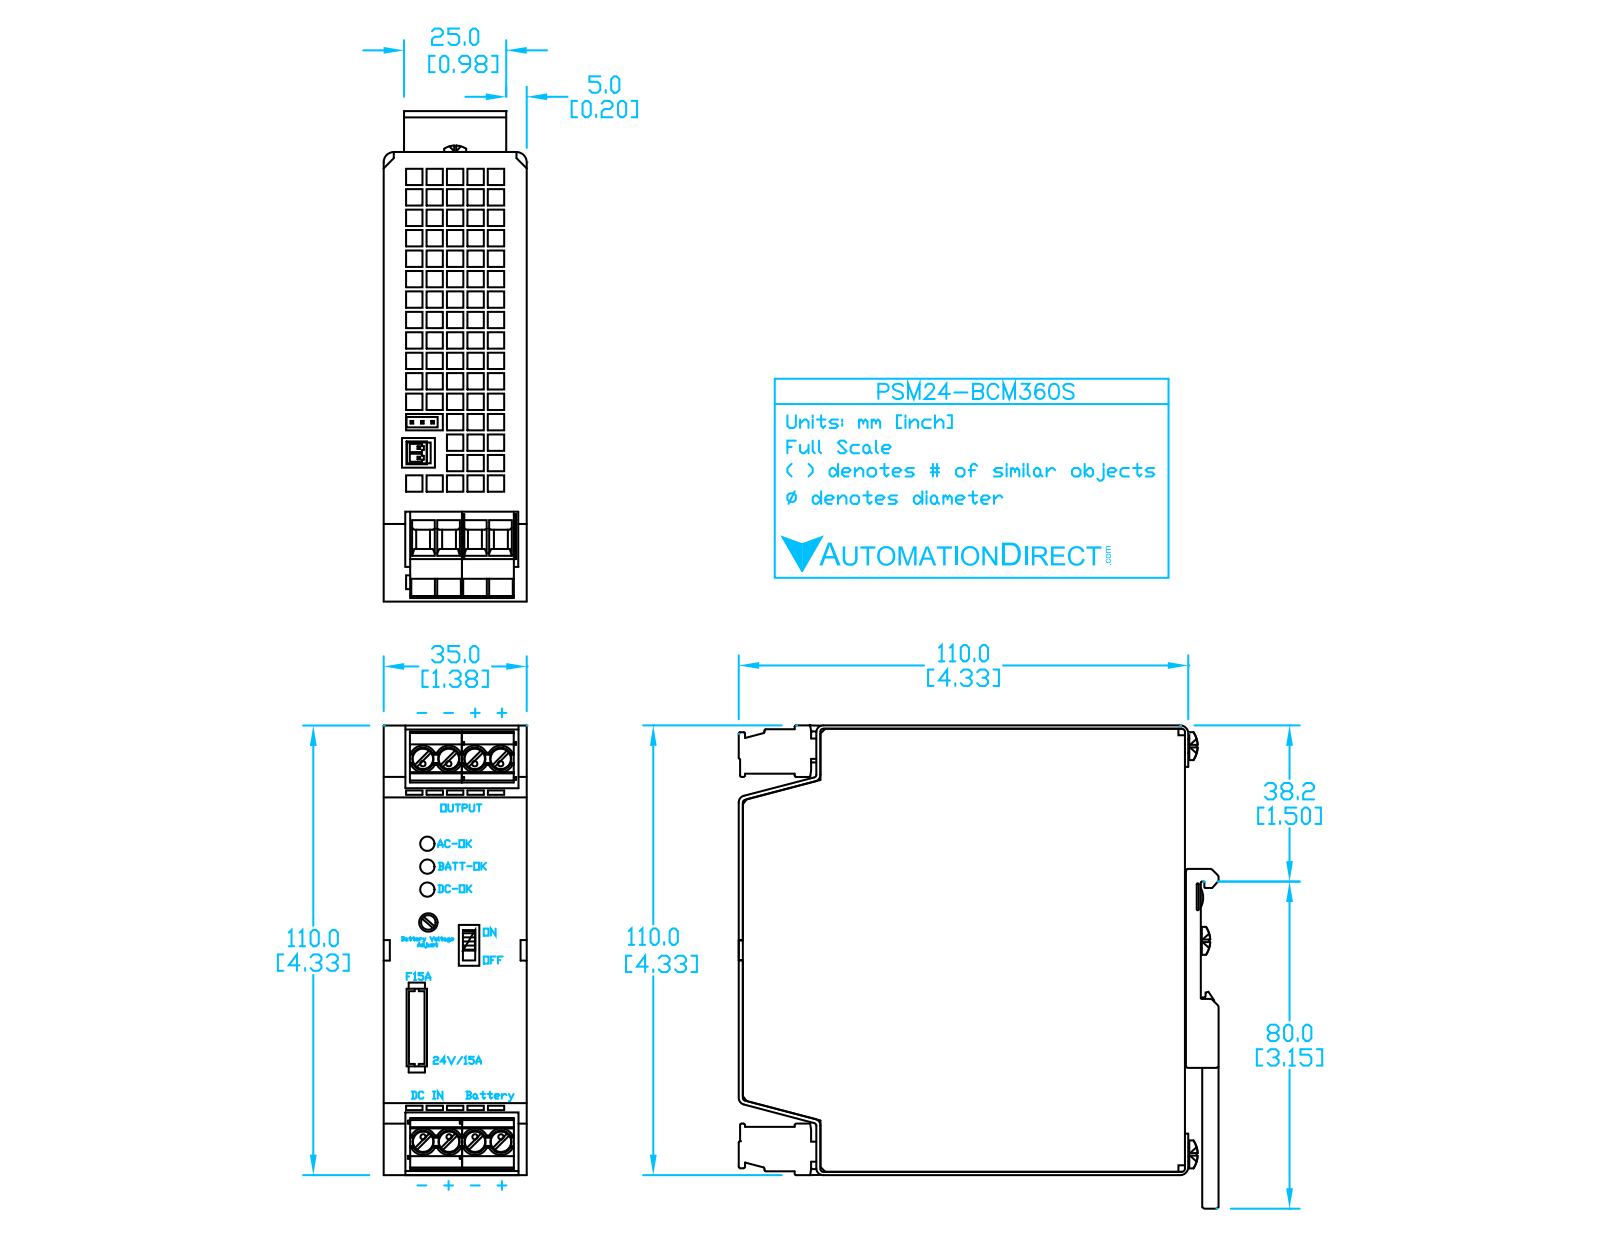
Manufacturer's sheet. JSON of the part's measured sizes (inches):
{"part_name": "PSM24-BCM360S", "step_written_by": "SolidWorks 2011 (CONFIG_CONTROL_DESIGN)", "units": "inches", "bodies": {"solids": 1, "faces": 1500, "planar": 1358, "cylindrical": 110, "other": 32}, "overall_size": [4.692, 4.691, 1.38], "volume_in3": 25.7, "surface_area_in2": 80.23, "round_holes": [[0.105, 10], [0.185, 8], [0.15, 5], [0.172, 1]], "round_bosses_or_shafts": [[0.11, 3], [0.21, 2], [0.265, 1], [0.041, 1], [0.041, 1]], "partial_cylinders_radius": [[0.025, 8], [0.04, 8], [0.06, 8], [0.02, 4], [0.03, 2], [0.07, 2], [0.081, 2]], "face_to_face_distances": [1.378, 0.04, 4.29, 4.33, 4.291, 3.74, 0.55, 3.78, 0.51, 4.25], "hole_center_spacings": [0.15, 0.3, 0.45, 0.6, 3.622, 0.75, 0.24, 0.48]}
